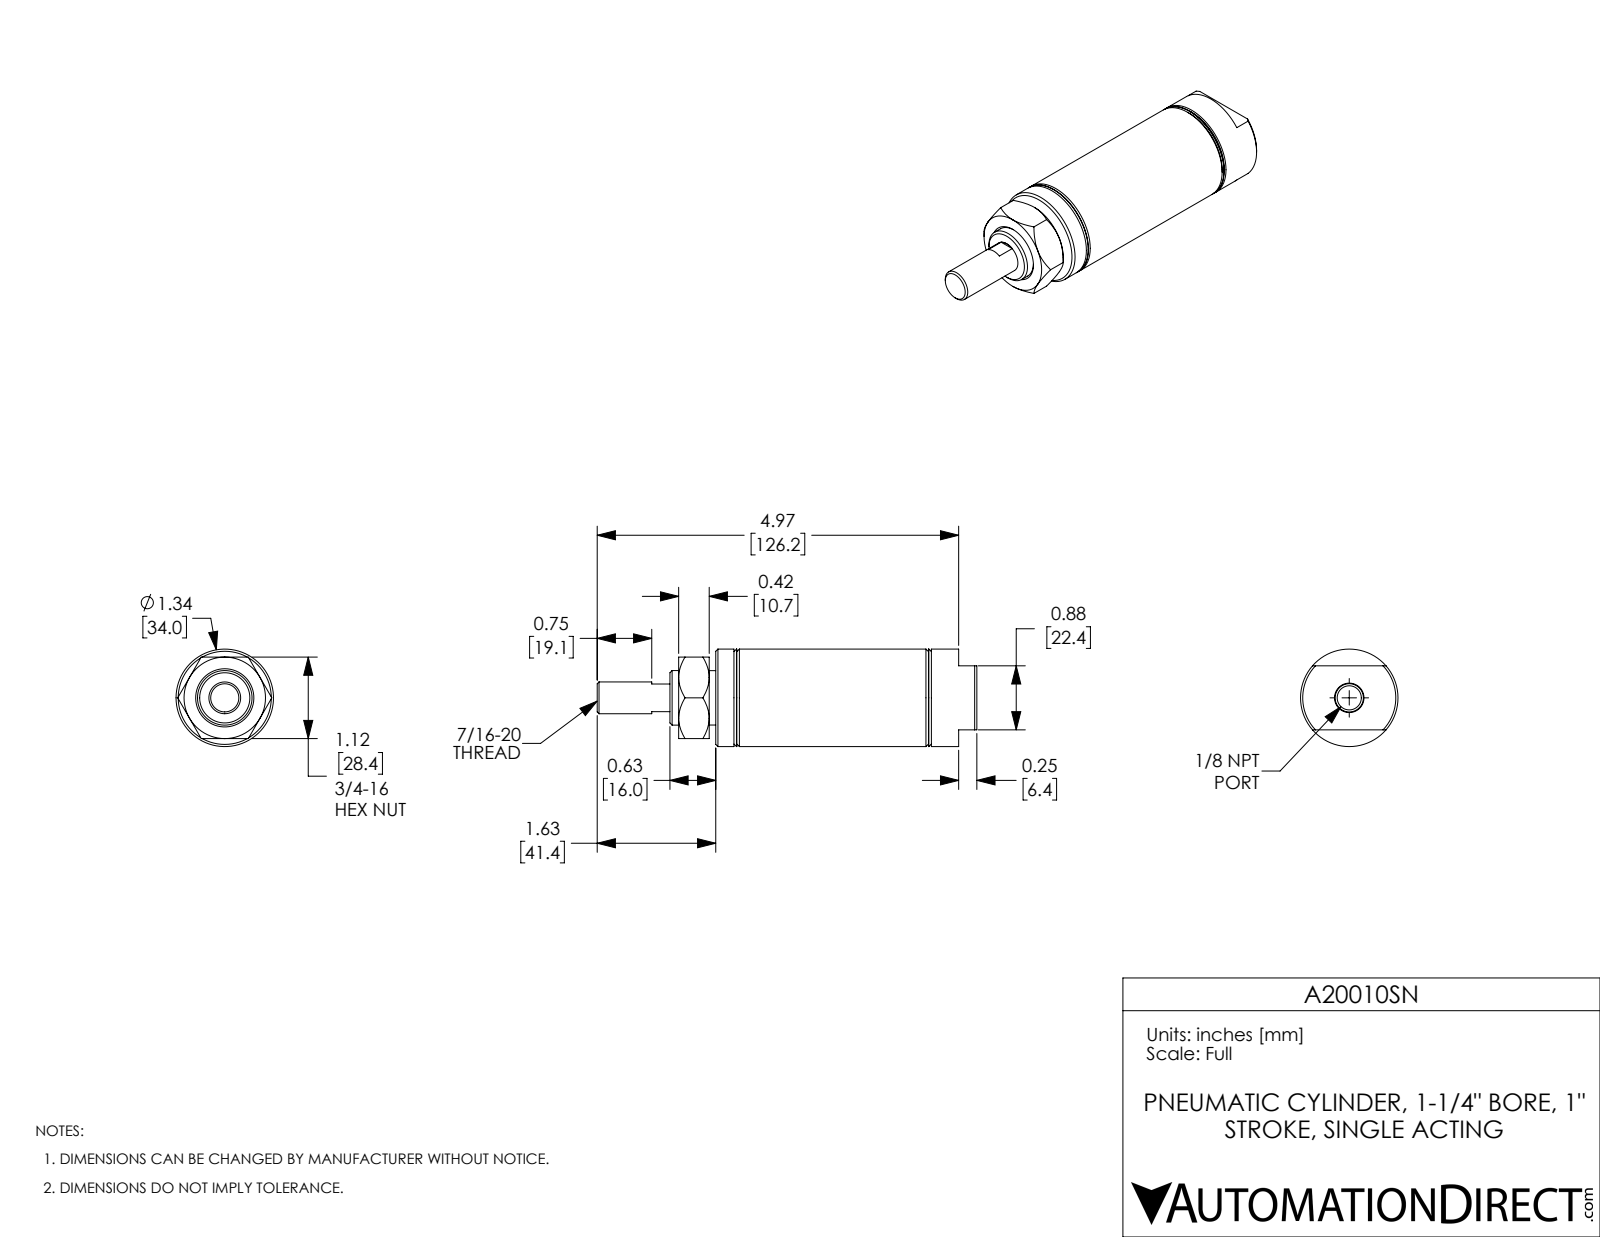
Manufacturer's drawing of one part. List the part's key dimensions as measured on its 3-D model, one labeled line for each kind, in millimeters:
Part name (STEP PRODUCT): A20010SN; A20010SN_Mounting Nut_D-3556; A20010SN-Rod; A20010SN-MainBody
STEP written by: SolidWorks 2017 (AUTOMOTIVE_DESIGN)
Units: millimetres
Bodies: 3 solids, 95 faces (32 planar, 26 cylindrical, 37 other)
Overall size (bounding box): 132.6 × 34 × 34
Volume: 74 220 mm³ · Surface area: 28 400 mm²
Round holes (diameter × count): ⌀8.4 ×1, ⌀11.1 ×1, ⌀19.1 ×1, ⌀31.8 ×1
Round bosses / shafts (diameter × count): ⌀34 ×1, ⌀19 ×1
Main face-to-face distances: 26.5, 64.6, 38.1, 38.1, 12.7, 12.7, 25.4, 26.5, 39.2, 91.2
